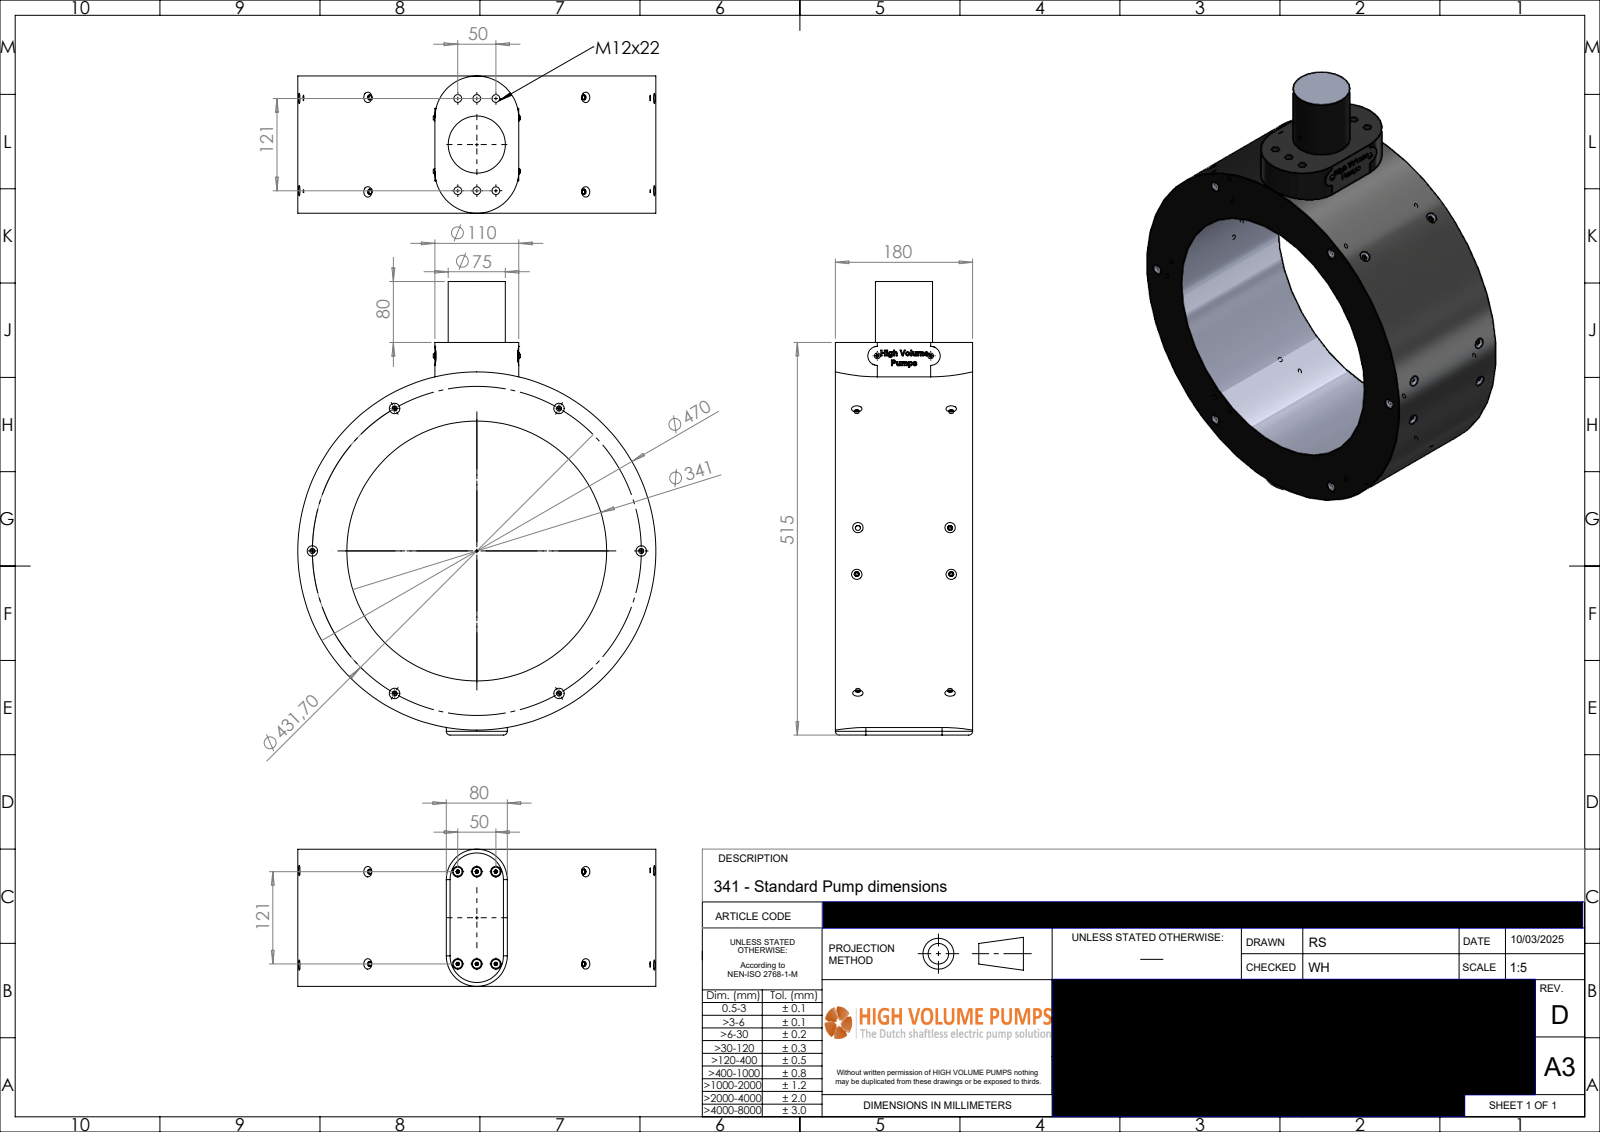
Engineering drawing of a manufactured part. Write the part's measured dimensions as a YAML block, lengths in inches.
part_name: "P-341-030-rev-D-SP"
step_written_by: "SolidWorks 2024 (AUTOMOTIVE_DESIGN)"
units: inches
bodies: {solids: 1, faces: 789, planar: 393, cylindrical: 88, other: 308}
overall_size: [23.427, 18.504, 7.087]
volume: 970.3
surface_area: 1058
round_holes:
  - {diameter: 0.26, count: 22}
  - {diameter: 0.197, count: 20}
  - {diameter: 0.402, count: 6}
  - {diameter: 13.425, count: 1}
round_bosses_or_shafts:
  - {diameter: 0.456, count: 6}
  - {diameter: 0.299, count: 2}
  - {diameter: 18.504, count: 1}
  - {diameter: 2.953, count: 1}
partial_cylinders:
  - {radius: 0.197, count: 2}
  - {radius: 0.492, count: 2}
  - {radius: 1.575, count: 2}
  - {radius: 2.165, count: 2}
face_to_face_distances: [7.087, 20.277, 3.15, 23.427, 4.331, 0.591, 3.74, 4.323, 0.583, 3.732]
hole_center_spacings: [8.498, 4.823, 4.764, 0.06, 0.061, 0.984, 4.865, 4.882]
